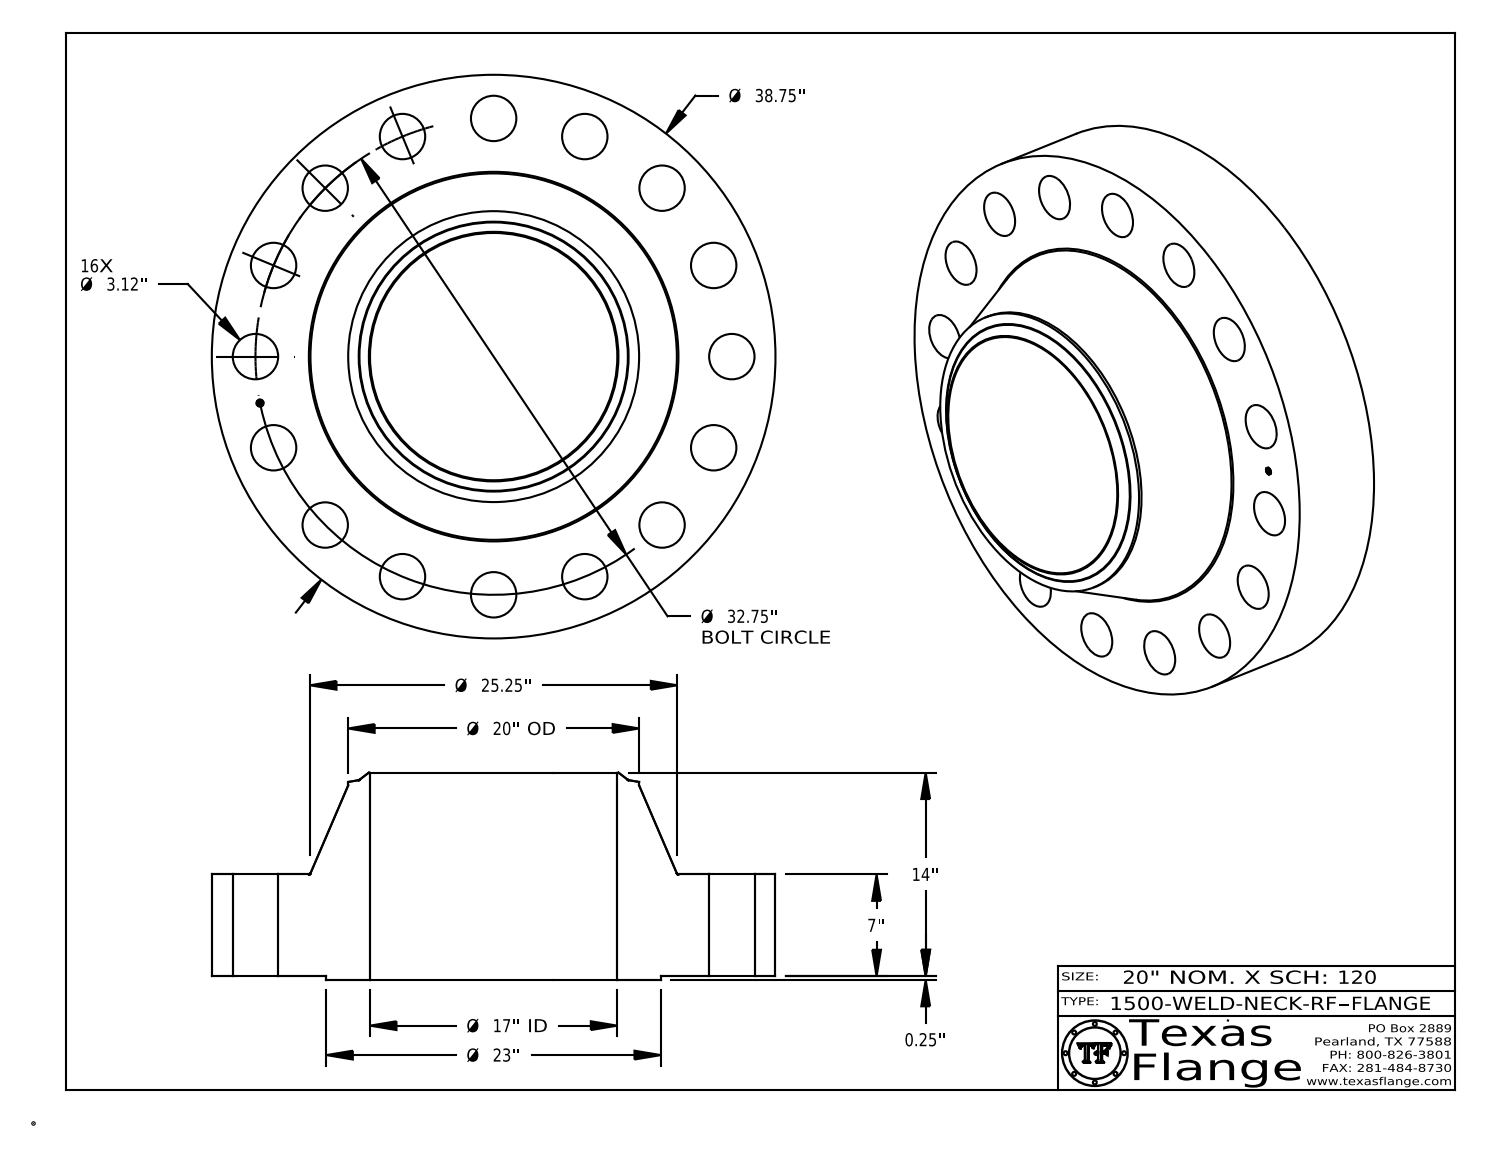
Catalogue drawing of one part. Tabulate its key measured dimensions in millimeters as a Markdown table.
| quantity | value |
| --- | --- |
| part name | 1500-WELD-NECK-RF |
| STEP written by | CATIA V5 STEP AP214 (AUTOMOTIVE_DESIGN) |
| units | millimeters |
| bodies | 1 solid, 439 faces (369 planar, 60 cylindrical, 10 other) |
| overall size | 984.3 × 984.3 × 362 |
| volume | 114 400 000 mm³ |
| surface area | 3 032 000 mm² |
| round holes (diameter × count) | 79.2 × 16, 12.6 × 1, 431.8 × 1 |
| round bosses / shafts (diameter × count) | 0.8 × 8, 984.3 × 1, 584.2 × 1, 508 × 1, 9.9 × 1 |
| main face-to-face distances | 177.8, 6.4, 184.2, 362, 355.6, 183.8, 177.4, 0.4, 178.2, 3.8 |
| hole center spacings | 462.2, 415.9, 318.3, 588.2, 768.5, 162.3, 162.3, 691.6 |
